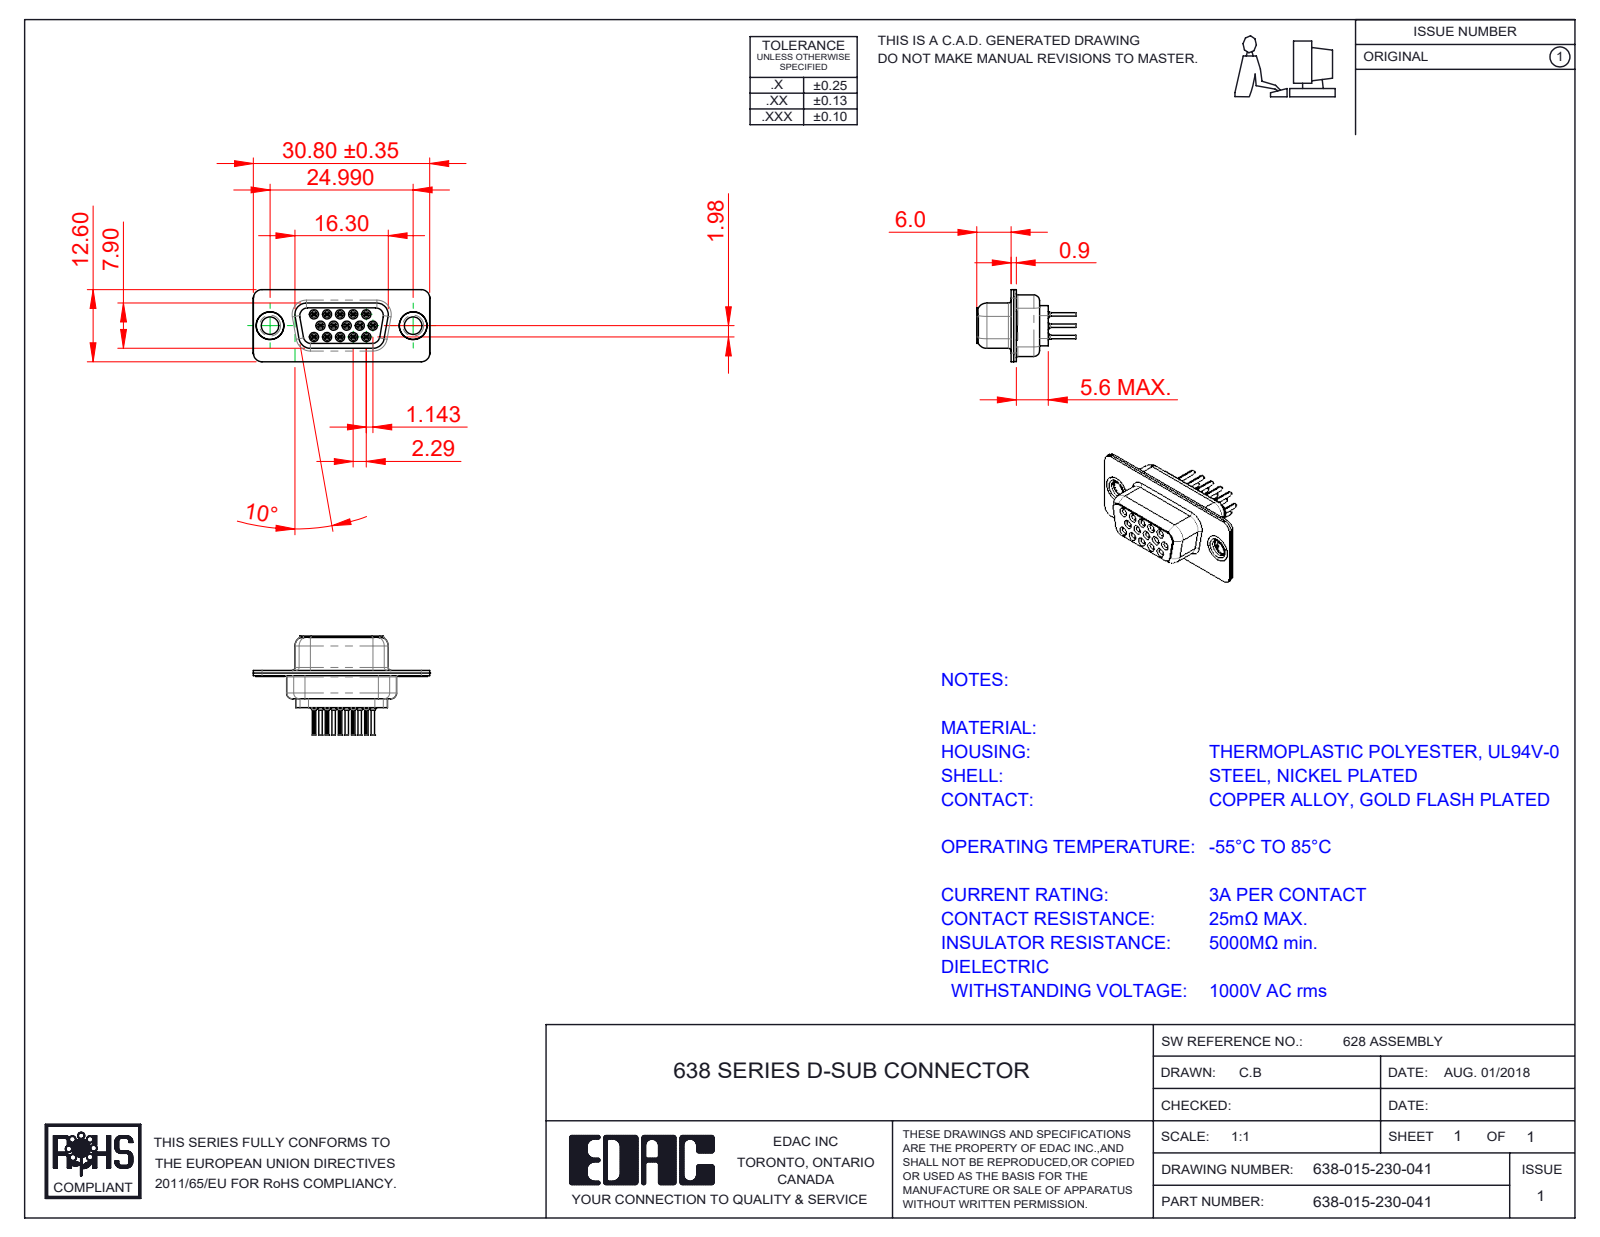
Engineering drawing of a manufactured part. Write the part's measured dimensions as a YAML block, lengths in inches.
part_name: "638 Contact Row 1_30; 638 Shell Front_15 Contacts; 638 Thru Hole Rivet; 638 Housing_15 Contacts (+4 more)"
step_written_by: "SolidWorks 2020 (CONFIG_CONTROL_DESIGN)"
units: inches
bodies: {solids: 20, faces: 2158, planar: 532, cylindrical: 616, other: 1010}
overall_size: [1.213, 0.681, 0.496]
volume: 0.091
surface_area: 8.451
round_holes:
  - {diameter: 0.008, count: 15}
  - {diameter: 0.031, count: 15}
  - {diameter: 0.039, count: 15}
  - {diameter: 0.043, count: 15}
  - {diameter: 0.063, count: 15}
  - {diameter: 0.067, count: 15}
  - {diameter: 0.071, count: 15}
  - {diameter: 0.079, count: 2}
  - {diameter: 0.12, count: 2}
  - {diameter: 0.157, count: 2}
  - {diameter: 0.159, count: 2}
  - {diameter: 0.191, count: 2}
round_bosses_or_shafts:
  - {diameter: 0.079, count: 15}
  - {diameter: 0.059, count: 15}
  - {diameter: 0.047, count: 15}
  - {diameter: 0.024, count: 15}
  - {diameter: 0.197, count: 2}
  - {diameter: 0.195, count: 2}
  - {diameter: 0.189, count: 2}
  - {diameter: 0.14, count: 2}
partial_cylinders:
  - {radius: 0.004, count: 30}
  - {radius: 0.059, count: 20}
  - {radius: 0.079, count: 12}
  - {radius: 0.011, count: 10}
  - {radius: 0.061, count: 8}
  - {radius: 0.053, count: 5}
  - {radius: 0.01, count: 4}
  - {radius: 0.02, count: 4}
face_to_face_distances: [0.018, 0.035, 0.016, 0.056, 0.35, 0.26, 0.055, 0.09, 0.278, 0.238]
hole_center_spacings: [0.156, 0.09, 0.18, 0.09, 0.238, 0.238, 0.27, 0.312]
